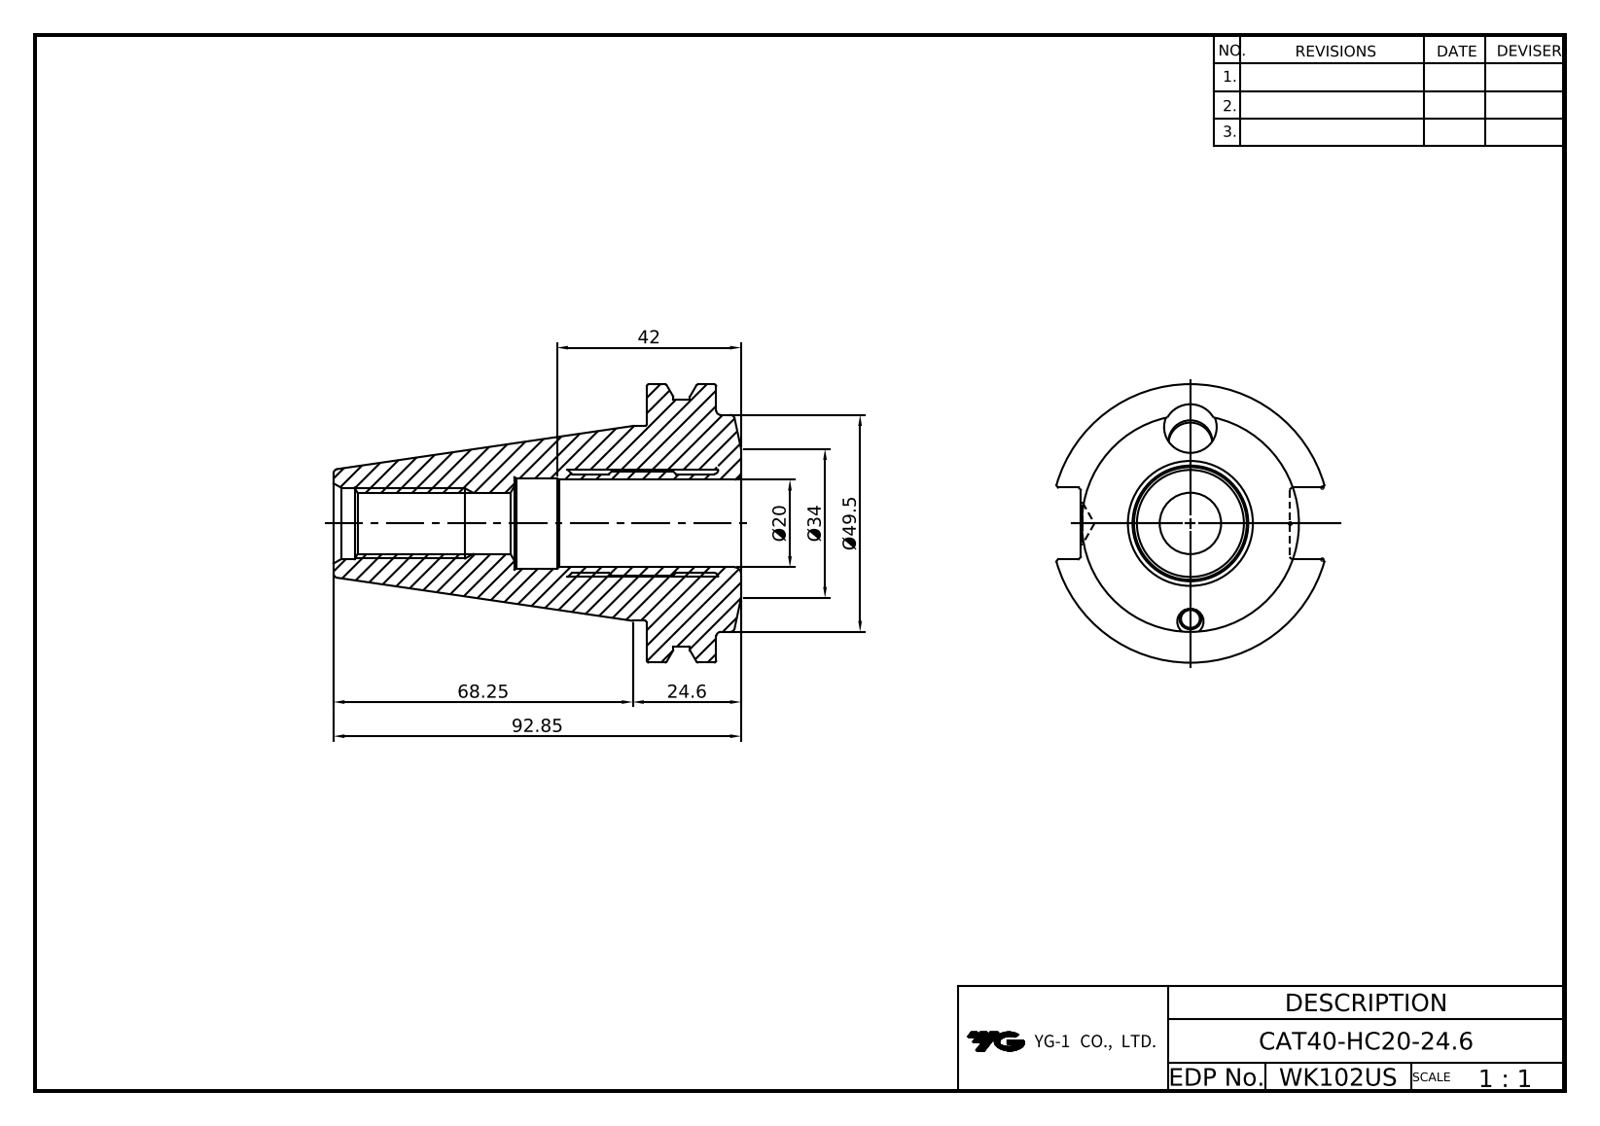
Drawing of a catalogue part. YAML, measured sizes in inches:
part_name: "LO-CAT40-HC20-24.6"
step_written_by: "Autodesk Inventor 2022 (AUTOMOTIVE_DESIGN)"
units: inches
bodies: {solids: 1, faces: 53, planar: 25, cylindrical: 12, other: 16}
overall_size: [3.656, 2.5, 2.405]
volume: 6.131
surface_area: 33.74
round_holes:
  - {diameter: 0.375, count: 1}
  - {diameter: 0.527, count: 1}
  - {diameter: 0.642, count: 1}
  - {diameter: 0.787, count: 1}
round_bosses_or_shafts:
  - {diameter: 2.5, count: 1}
  - {diameter: 2.217, count: 1}
  - {diameter: 1.949, count: 1}
  - {diameter: 1.75, count: 1}
face_to_face_distances: [0.625, 0.844, 0.219, 1.874, 1.192, 1.817, 2.035, 0.645, 1.62, 2.812]
